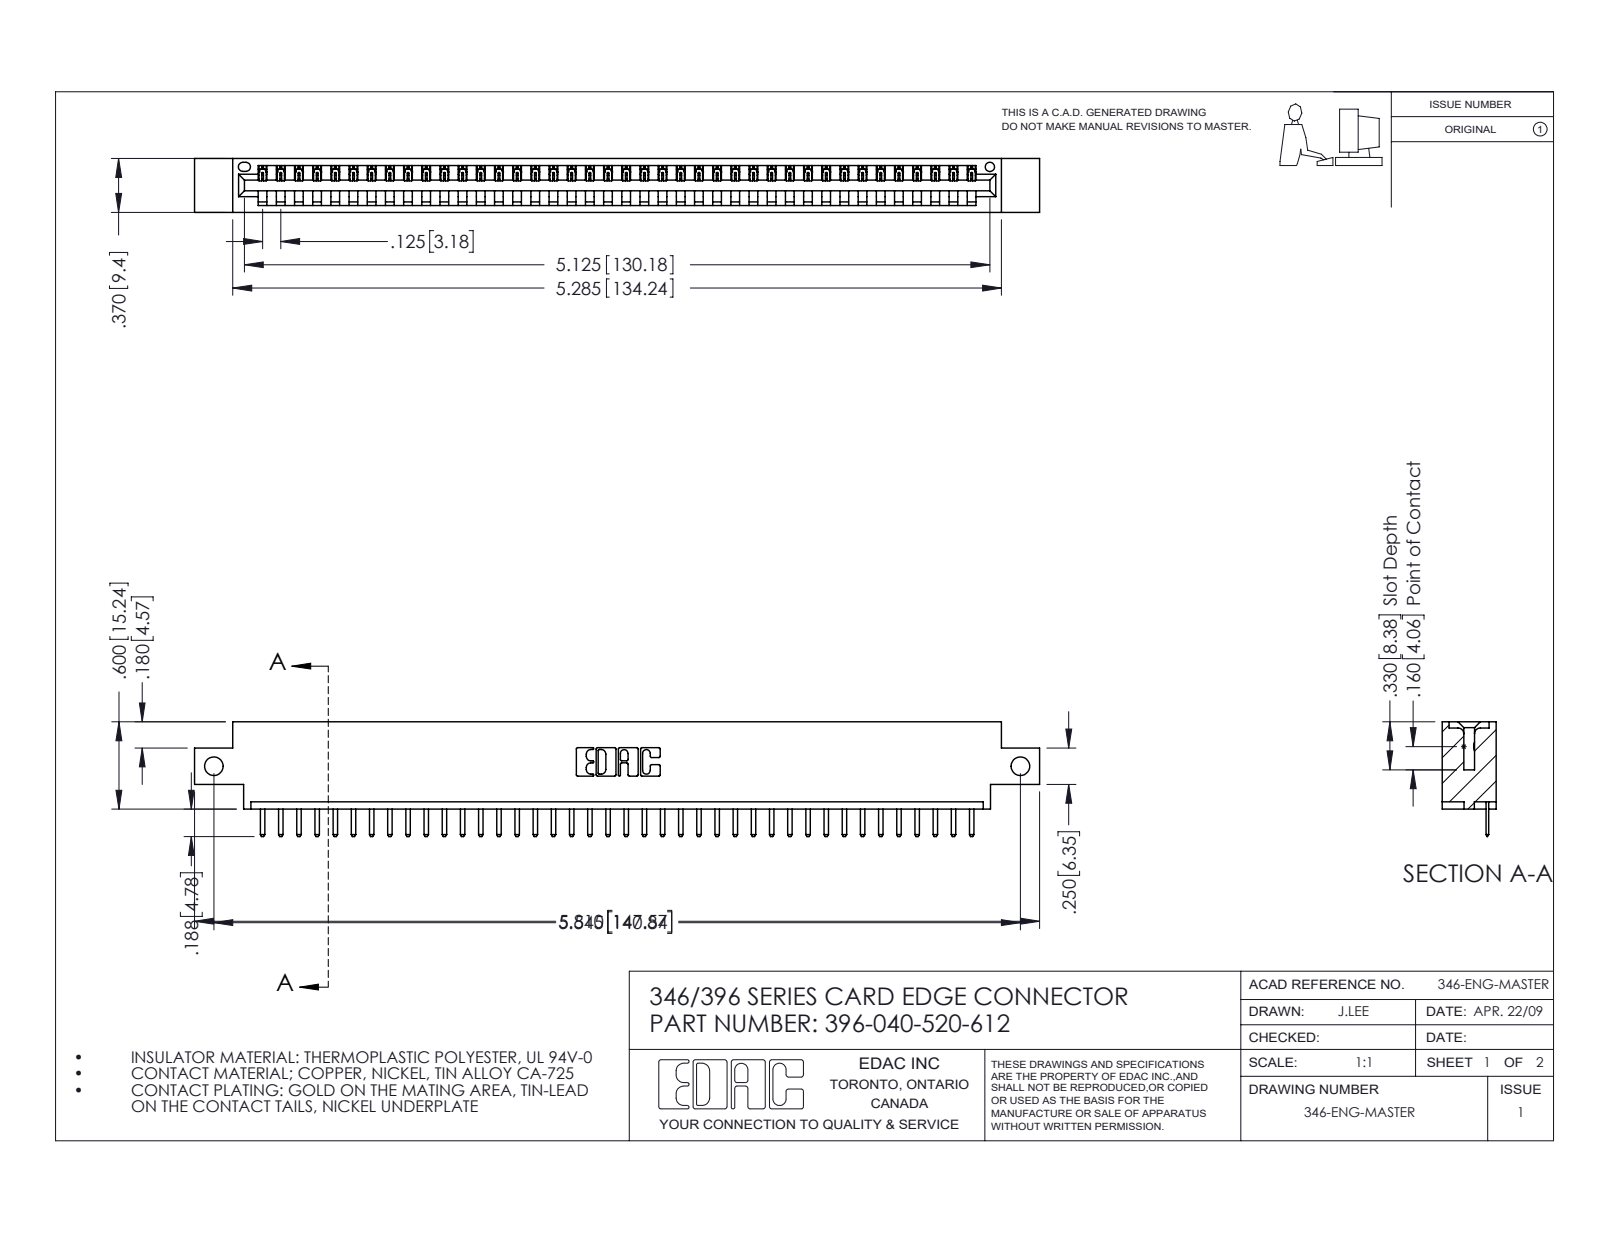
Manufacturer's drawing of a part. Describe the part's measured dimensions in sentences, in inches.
The part is named "345-292-001_345-293-120; 396-040-520-612; 346 Part_0.170 Offset - Side Mount". Its 3-D file was written by "SolidWorks 2016 (CONFIG_CONTROL_DESIGN)". It is 41 solids with 2606 faces: 1760 planar, 846 cylindrical and 0 other. Overall it measures 5.81 by 0.788 by 0.37 inches. Its volume is 0.839 cubic inches and its surface area 26.04 square inches. Round holes: 2 of diameter 0.128, 1 of diameter 0.064. Partial cylindrical surfaces (rounded edges, fillets, slot ends): 82 of radius 0.01, 80 of radius 0.006, 22 of radius 0.01, 6 of radius 0.007, 6 of radius 0.031, 3 of radius 0.026, 2 of radius 0.031, 2 of radius 0.04. The main face-to-face distances are 0.048, 0.322, 0.37, 0.25, 0.148, 0.222, 0.1, 0.174, 0.072, 0.298. The hole center spacings are 5.545.
